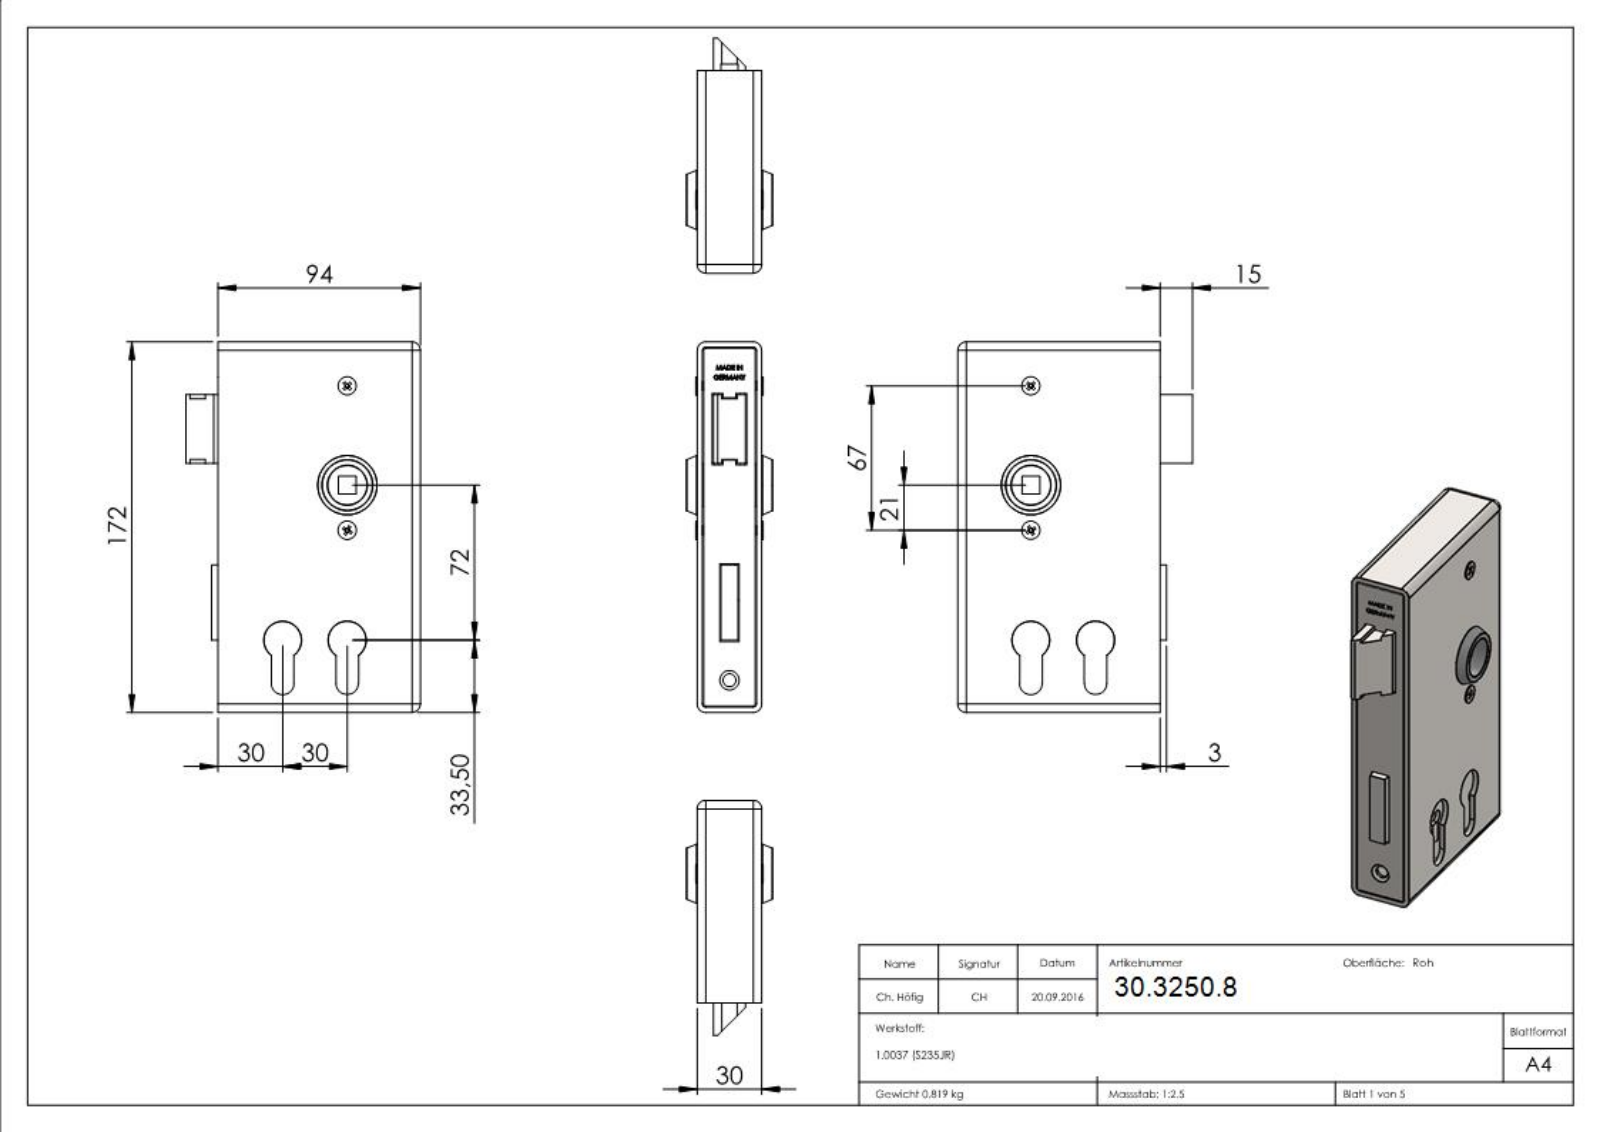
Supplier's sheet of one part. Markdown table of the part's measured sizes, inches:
| quantity | value |
| --- | --- |
| part name | 11163 Teil1_11163; 3810-GS; countersunk flat head cross recess screw_din; 11163 Teil1 (+4 more) |
| STEP written by | SolidWorks 2018 (CONFIG_CONTROL_DESIGN) |
| units | inches |
| bodies | 13 solids, 839 faces (487 planar, 141 cylindrical, 211 other) |
| overall size | 6.772 × 4.291 × 1.575 |
| volume | 11.09 in³ |
| surface area | 240.4 in² |
| round holes (diameter × count) | 0.13 × 2, 0.165 × 2, 0.207 × 2, 0.689 × 2, 0.693 × 2, 0.228 × 1, 0.236 × 1, 0.248 × 1, 0.256 × 1, 0.315 × 1, 0.331 × 1, 0.717 × 1 |
| round bosses / shafts (diameter × count) | 0.331 × 2, 0.217 × 2, 0.157 × 2, 0.827 × 1, 0.795 × 1 |
| partial cylindrical surfaces (radius × count) | 0.118 × 16, 0.059 × 8, 0.157 × 8, 0.394 × 6, 0.108 × 4, 0.207 × 4, 0.039 × 2, 0.079 × 2 |
| main face-to-face distances | 0.098, 0.394, 1.083, 0.315, 0.787, 0.295, 0.472, 0.768, 0.866, 0.079 |
| hole center spacings | 0.325, 0.402, 0.508, 0.739, 0.76, 0.827, 0.866, 1.033 |
